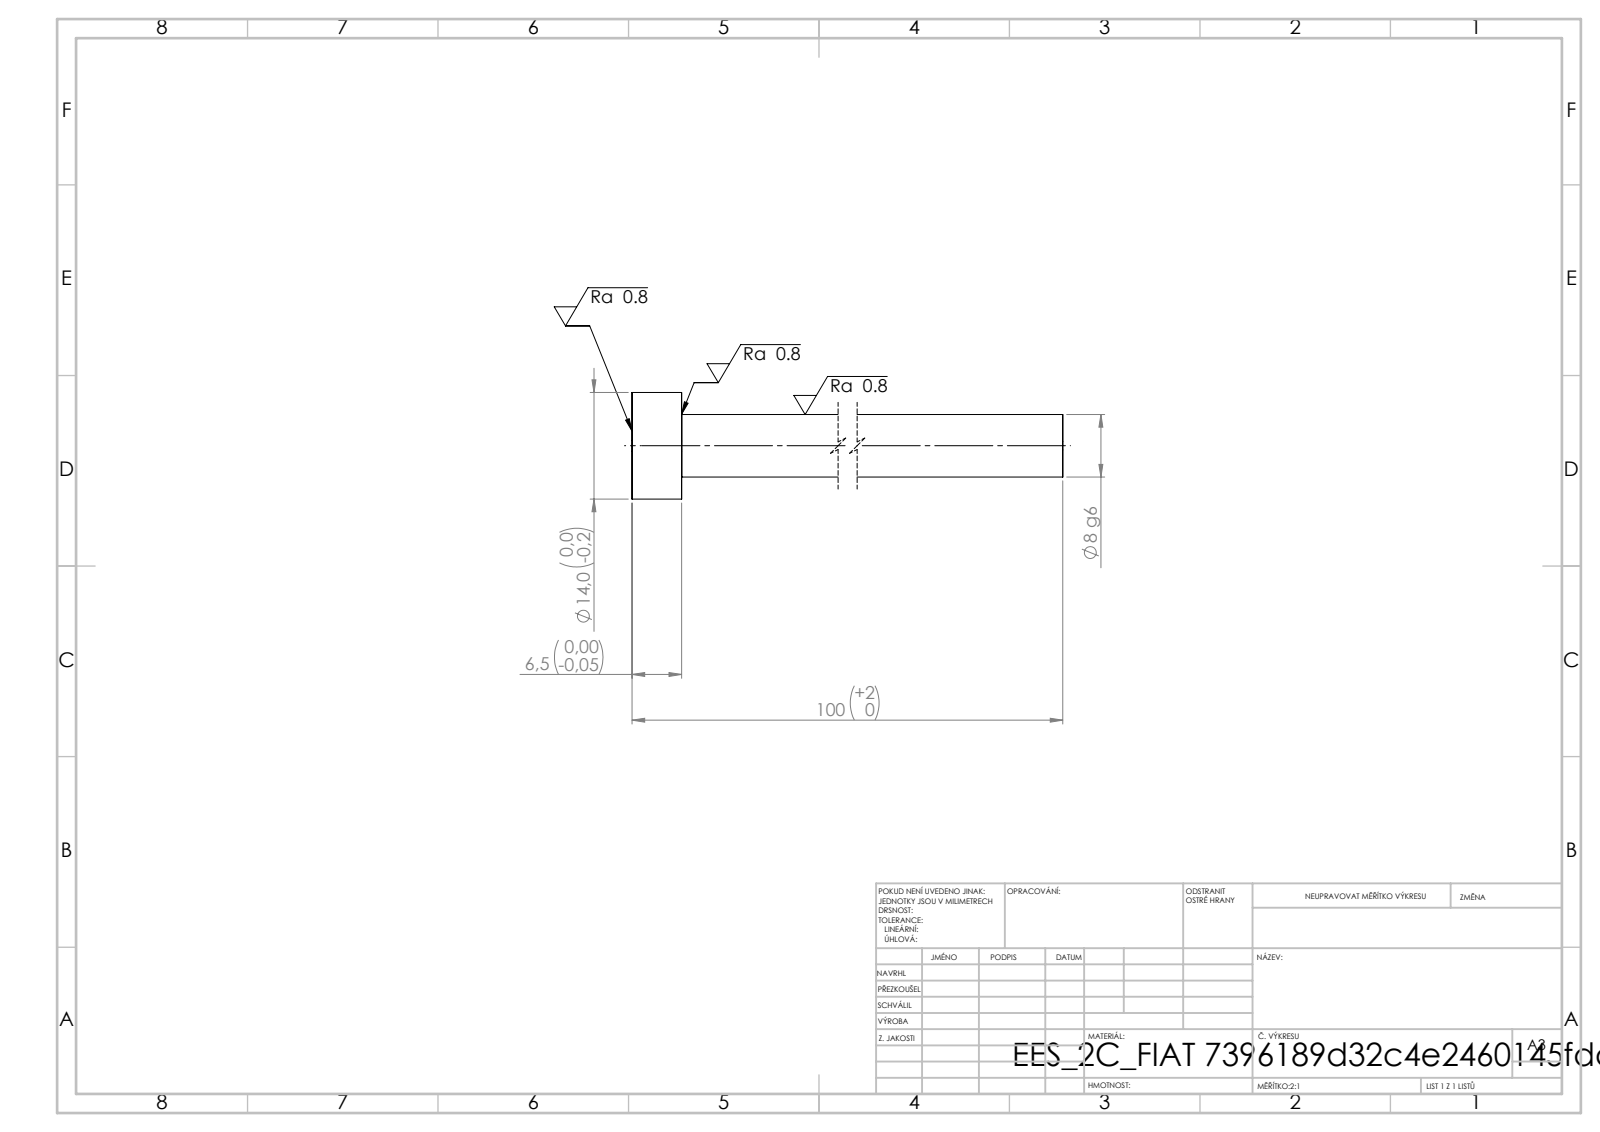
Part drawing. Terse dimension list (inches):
written by: SolidWorks 2019 (CONFIG_CONTROL_DESIGN)
unit: in
bodies: 1 solid, 7 faces (3 planar, 4 cylindrical, 0 other)
size: 3.937 × 0.551 × 0.551
volume: 0.362 in³; area: 4.653 in²
bosses: 1× ⌀0.551, 1× ⌀0.323
face distances: 0.256, 3.937, 3.681
